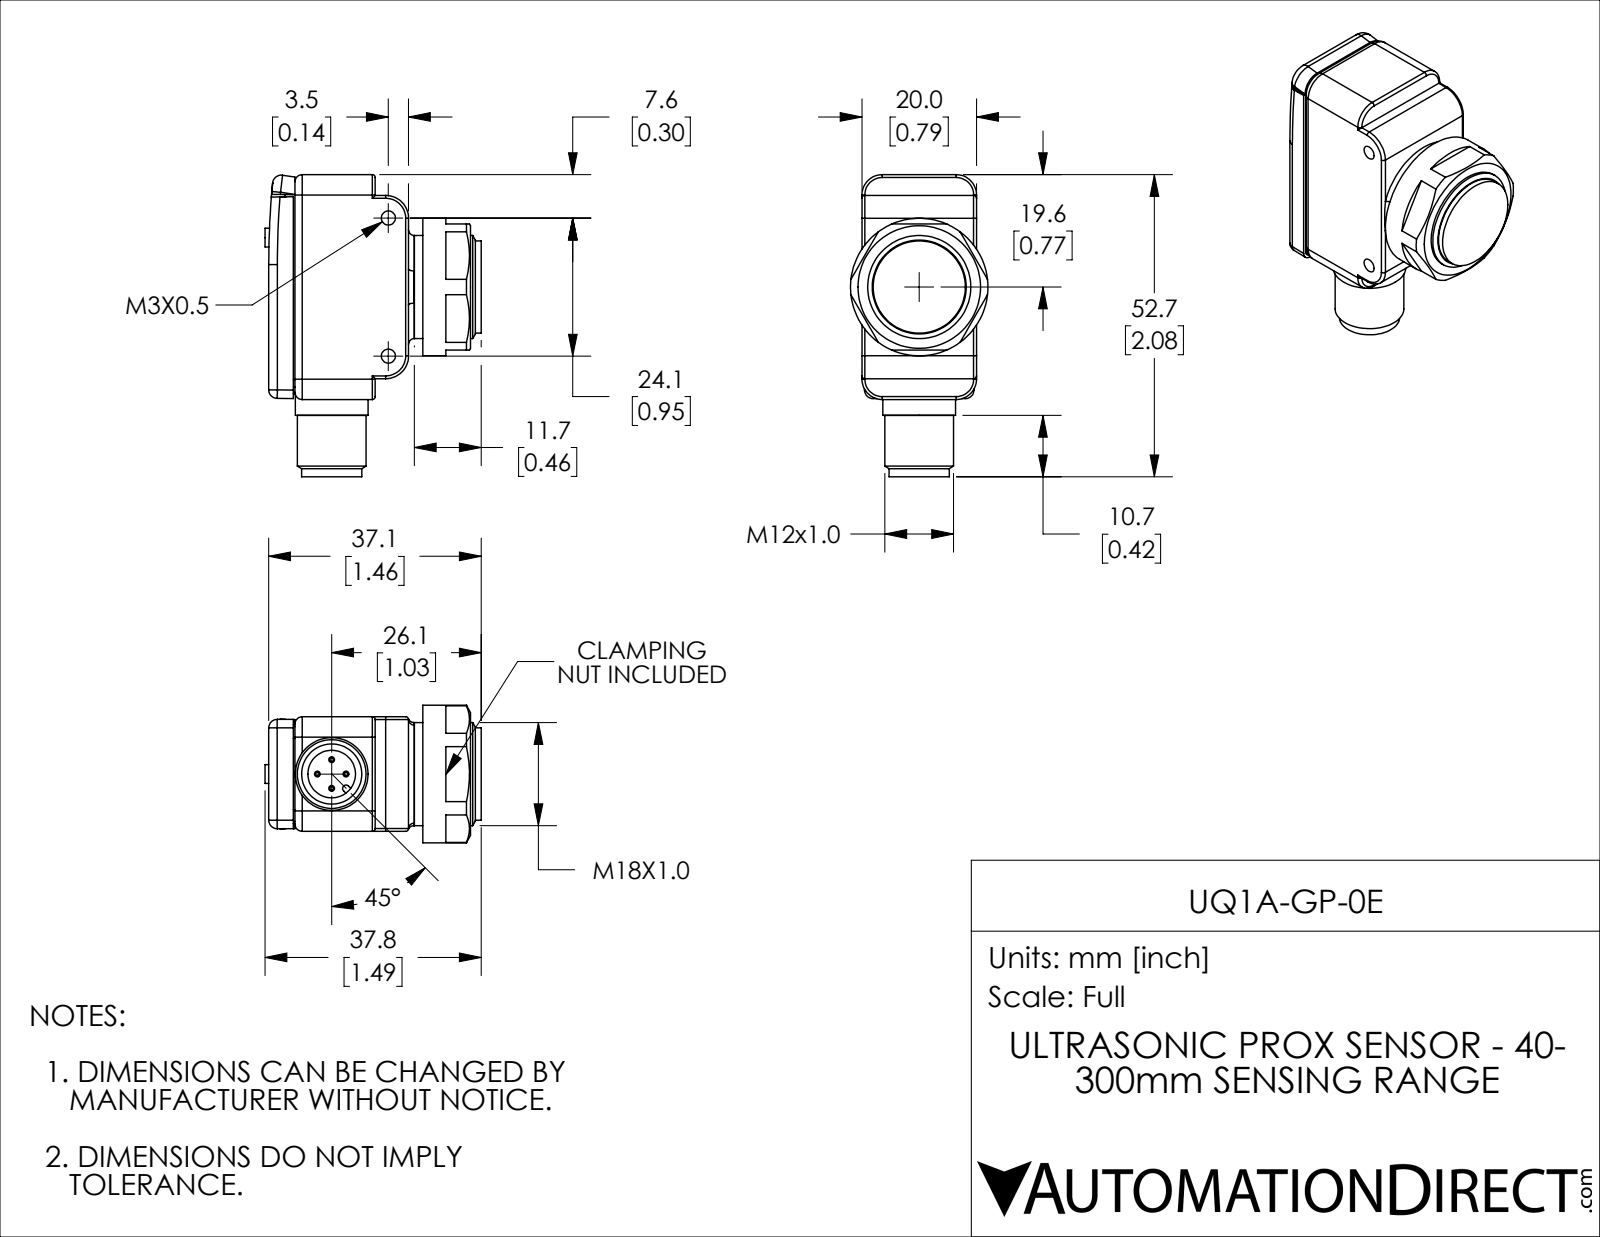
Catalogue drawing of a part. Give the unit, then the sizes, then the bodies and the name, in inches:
Units: inches
Overall size (bounding box): 2.076 × 1.486 × 0.945
Round holes (diameter × count): ⌀0.097 ×2, ⌀0.13 ×1, ⌀0.327 ×1
Round bosses / shafts (diameter × count): ⌀0.039 ×4, ⌀0.945 ×1, ⌀0.709 ×1, ⌀0.634 ×1, ⌀0.5 ×1, ⌀0.472 ×1, ⌀0.413 ×1
Partial cylindrical surfaces — rounded edges, fillets, slot ends (radius × count): R0.02 ×10, R0.059 ×6, R0.049 ×4, R0.14 ×4, R0.118 ×2, R0.157 ×2, R5.906 ×2, R0.024 ×1
Main face-to-face distances: 0.091, 0.787, 0.911, 0.82, 0.09, 0.181, 1.001, 0.459, 1.46, 1.37
Hole centre spacings: 0.949
Volume: 1.389 in³ · Surface area: 17.13 in²
Bodies: 7 solids, 203 faces (81 planar, 72 cylindrical, 50 other)
Part name (STEP PRODUCT): UQ1A-GP-0E
STEP written by: SolidWorks 2018 (AUTOMOTIVE_DESIGN)
